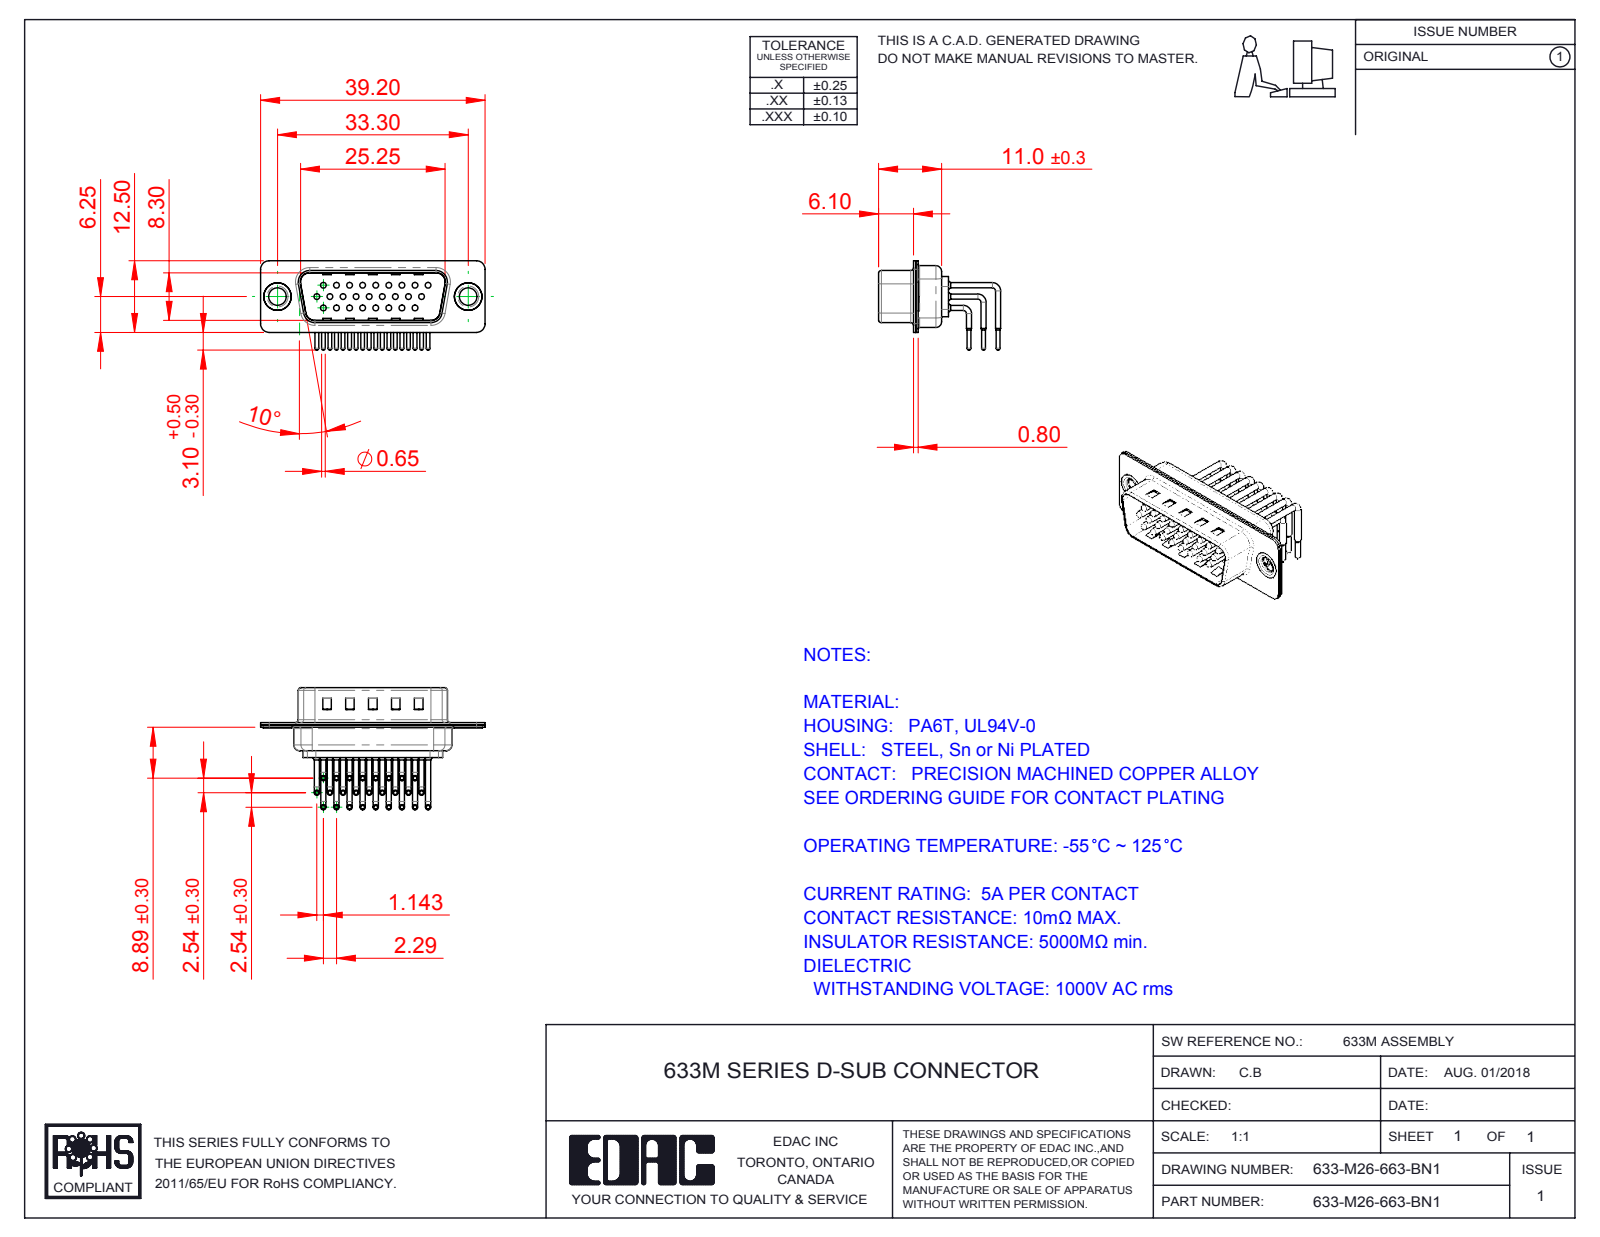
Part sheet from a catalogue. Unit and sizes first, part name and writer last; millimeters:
Units: millimetres
Overall size (bounding box): 39.2 × 21.32 × 15.6
Round holes (diameter × count): ⌀1 ×26, ⌀1.7 ×26, ⌀2 ×26, ⌀3.05 ×2, ⌀4 ×2, ⌀4.8 ×2
Round bosses / shafts (diameter × count): ⌀0.9 ×52, ⌀1.5 ×26, ⌀0.65 ×26, ⌀5 ×2, ⌀4.9 ×2, ⌀3.55 ×2
Partial cylindrical surfaces — rounded edges, fillets, slot ends (radius × count): R1.01 ×26, R1.5 ×16, R2 ×12, R0.5 ×8, R1.6 ×8, R0.25 ×4, R0.6 ×4, R0.65 ×4
Main face-to-face distances: 0.4, 0.85, 9.55, 1.5, 8.7, 1.9, 1.25, 0.8, 10.4, 0.35
Hole centre spacings: 3.96, 2.28, 4.57, 6.05, 2.29, 8.24, 6.86, 10.48
Volume: 2 011 mm³ · Surface area: 6 546 mm²
Bodies: 31 solids, 3174 faces (1803 planar, 1053 cylindrical, 318 other)
Part name (STEP PRODUCT): 633M Contact Row 1; 633M Contact Row 2; 633M Housing_26 Contacts; 633M Shell Front_26 Contacts (+4 more)
STEP written by: SolidWorks 2016 (CONFIG_CONTROL_DESIGN)
